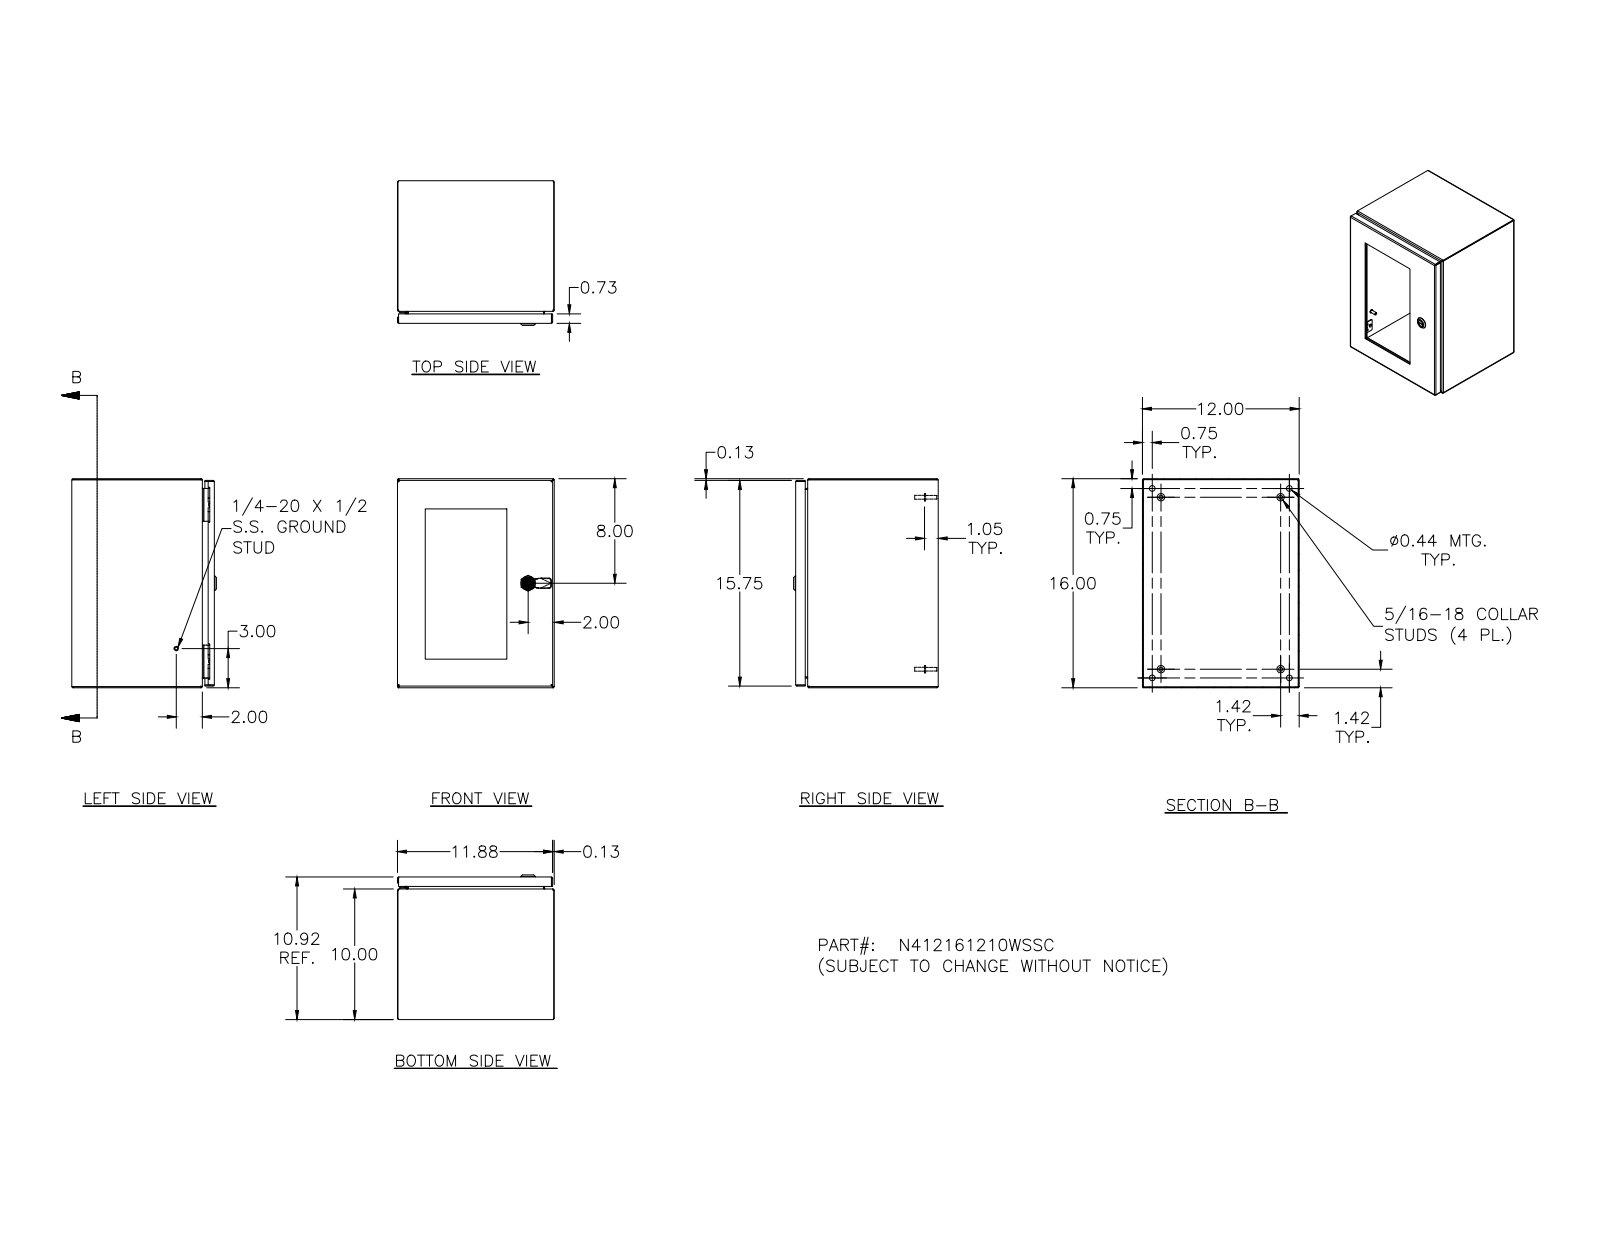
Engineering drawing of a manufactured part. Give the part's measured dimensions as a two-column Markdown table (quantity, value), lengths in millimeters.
| quantity | value |
| --- | --- |
| part name | N412161210WSSC; N412161210WSSCBKP; N4121612WSSCLID; HFW328176 (+8 more) |
| STEP written by | Autodesk Inventor 2011 (AUTOMOTIVE_DESIGN) |
| units | millimeters |
| bodies | 58 solids, 1748 faces (688 planar, 541 cylindrical, 519 other) |
| overall size | 406.4 × 304.8 × 281.3 |
| volume | 1 629 000 mm³ |
| surface area | 1 479 000 mm² |
| round holes (diameter × count) | 4 × 12, 7.1 × 10, 2.4 × 4, 3.9 × 4, 4.2 × 4, 4.4 × 4, 4.8 × 4, 11.1 × 4, 4.7 × 1, 5 × 1, 8 × 1, 10 × 1 |
| round bosses / shafts (diameter × count) | 6.4 × 10, 4.8 × 10, 6.4 × 9, 14.3 × 4, 9.1 × 4, 8.1 × 4, 7.6 × 4, 7 × 4 |
| partial cylindrical surfaces (radius × count) | 0.8 × 34, 1.3 × 26, 2.7 × 24, 0.4 × 18, 3.2 × 16, 0.5 × 9, 0.8 × 8, 4 × 4 |
| main face-to-face distances | 1.9, 302.9, 275.4, 404.5, 273.5, 301, 304.8, 406.4, 402.6, 277.3 |
| hole center spacings | 101.6, 304.8, 158, 215.9, 218.1, 301.3, 190.5, 12.7 |
